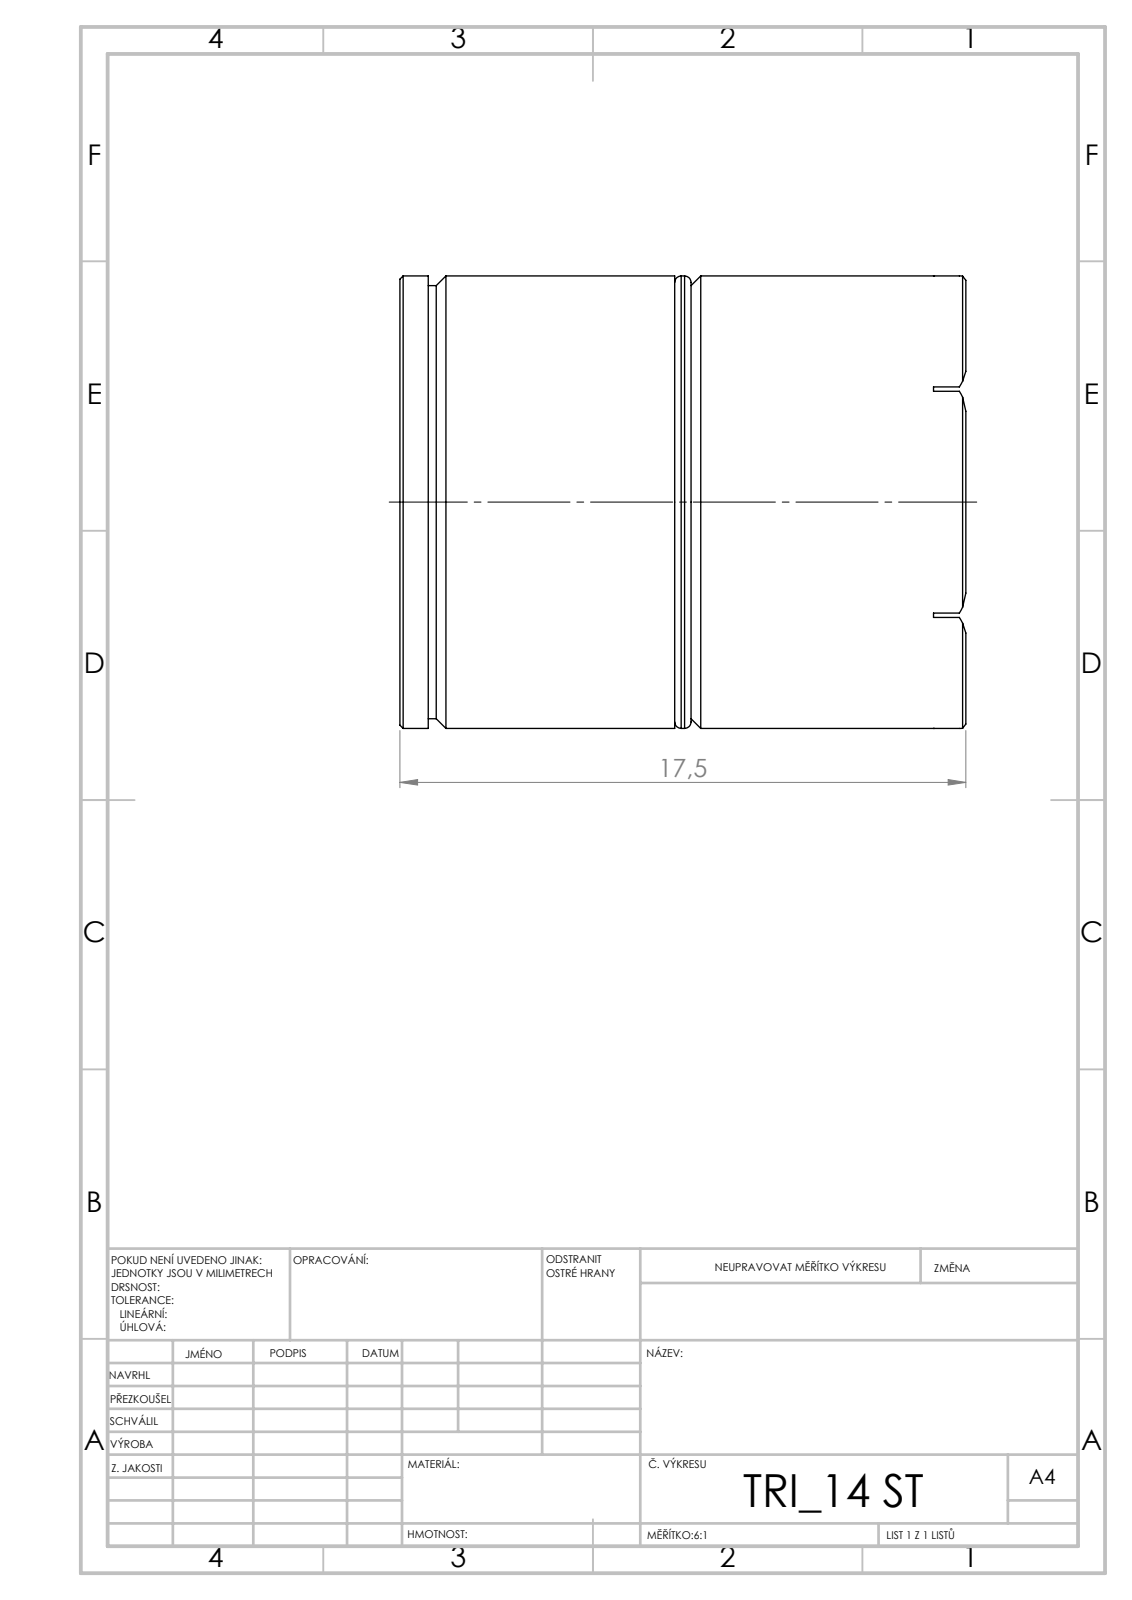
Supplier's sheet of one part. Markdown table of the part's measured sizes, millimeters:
| quantity | value |
| --- | --- |
| STEP written by | SolidWorks 2019 (CONFIG_CONTROL_DESIGN) |
| units | millimeters |
| bodies | 2 solids, 53 faces (24 planar, 12 cylindrical, 17 other) |
| overall size | 17.5 × 14 × 14 |
| volume | 2 626 mm³ |
| surface area | 1 464 mm² |
| round bosses / shafts (diameter × count) | 14 × 1, 13.4 × 1 |
| main face-to-face distances | 8.5, 9, 0.5, 7.5, 8, 16.5, 12.2, 1, 17.5, 16.63 |
